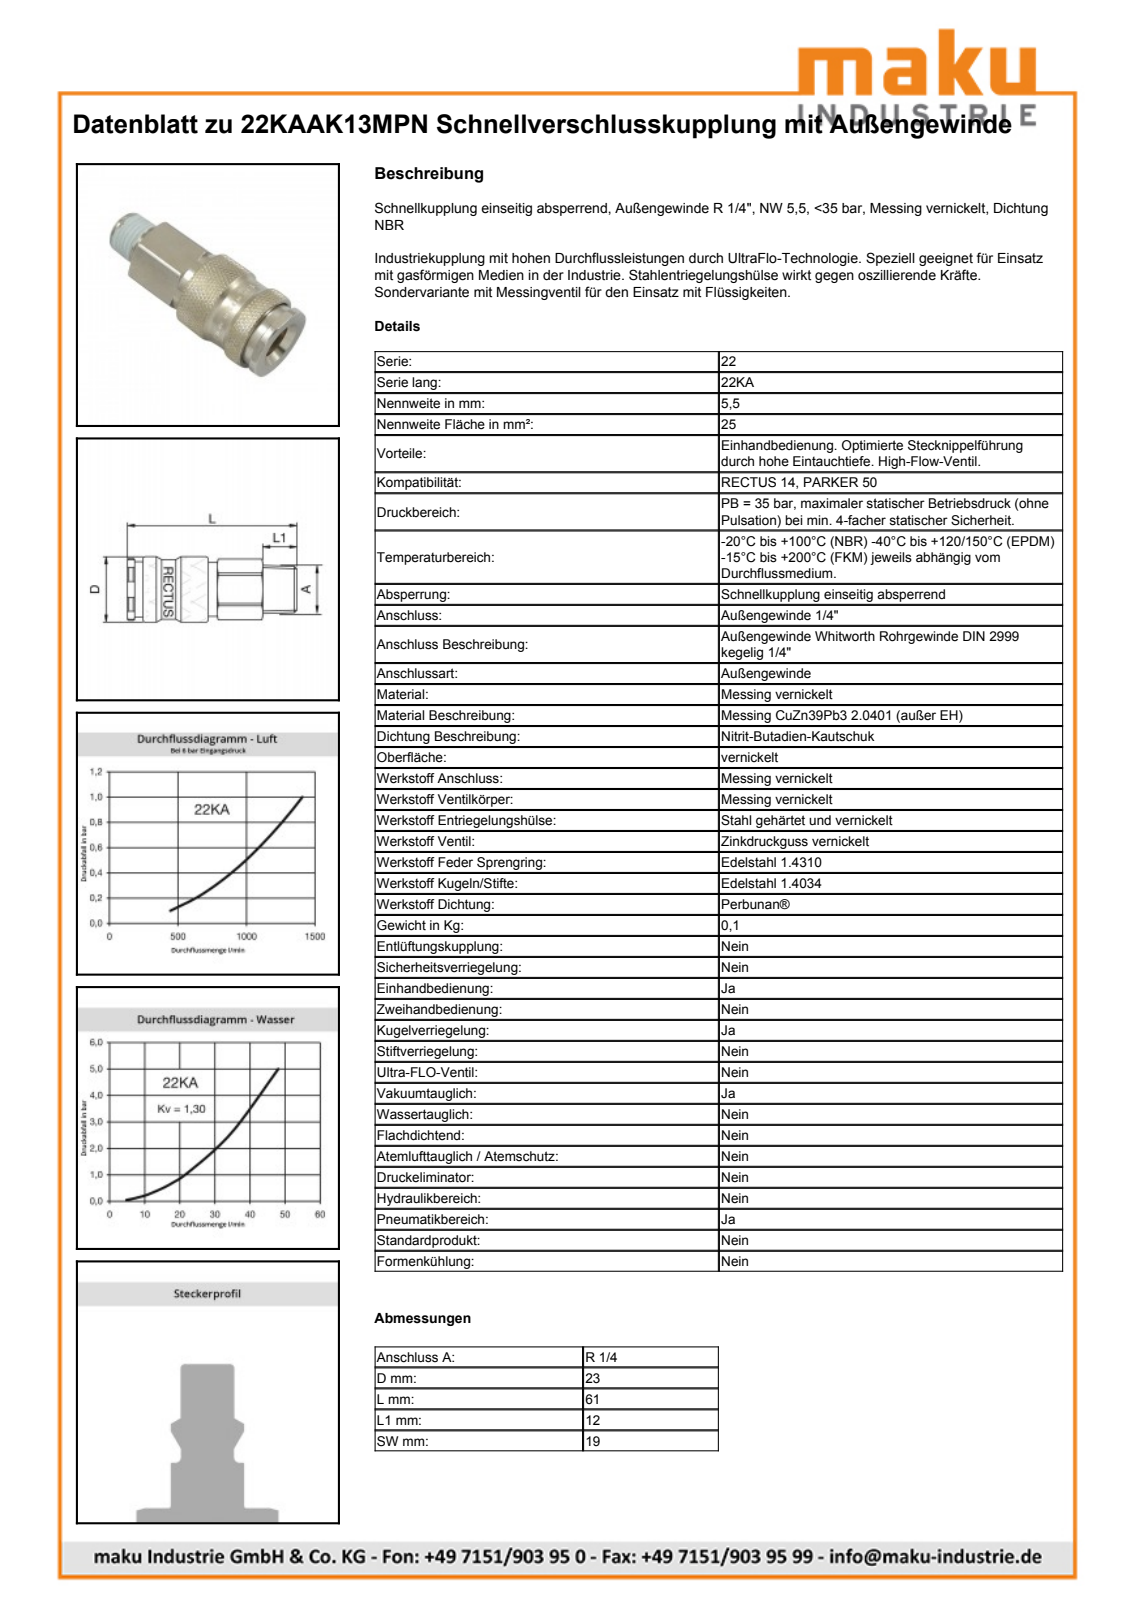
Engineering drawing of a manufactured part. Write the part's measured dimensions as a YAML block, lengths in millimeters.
part_name: "D109324"
step_written_by: "Autodesk Inventor 2013 (AUTOMOTIVE_DESIGN)"
units: millimeters
bodies: {solids: 2, faces: 518, planar: 170, cylindrical: 60, other: 288}
overall_size: [60.6, 23.15, 23.15]
volume: 17687
surface_area: 7534
round_holes:
  - {diameter: 16.95, count: 1}
  - {diameter: 19.35, count: 1}
  - {diameter: 19.65, count: 1}
round_bosses_or_shafts:
  - {diameter: 23.15, count: 1}
  - {diameter: 21, count: 1}
  - {diameter: 19.4, count: 1}
  - {diameter: 18.95, count: 1}
  - {diameter: 16.24, count: 1}
partial_cylinders:
  - {radius: 10.4, count: 1}
  - {radius: 10.7, count: 1}
  - {radius: 11, count: 1}
face_to_face_distances: [19, 48.6, 60.6, 12, 24.6, 24, 36, 20, 4.6, 28.6]
